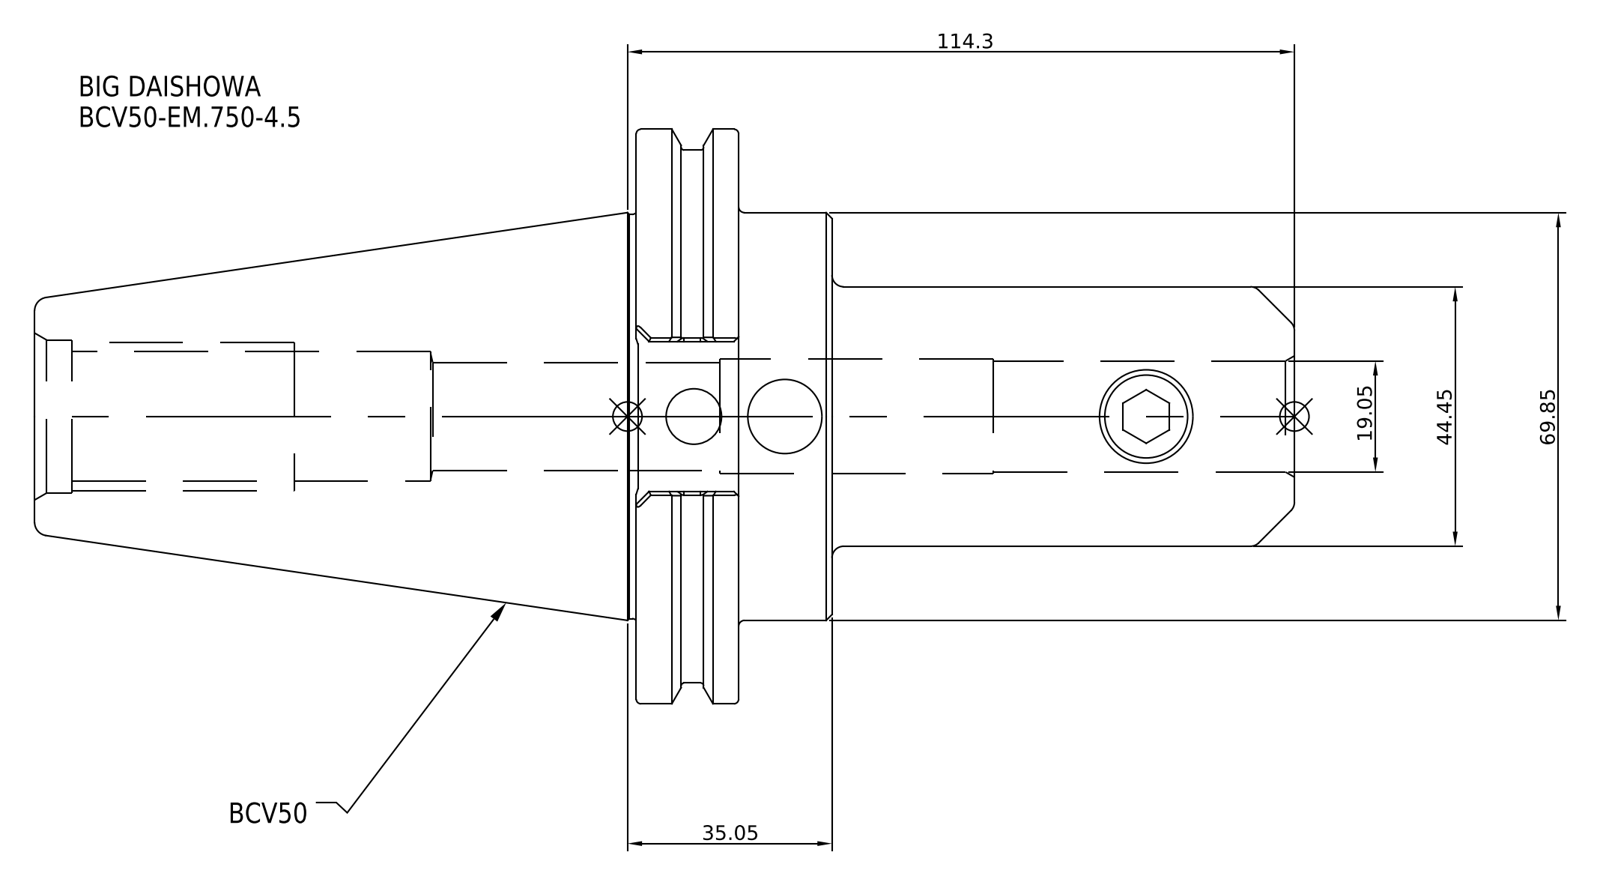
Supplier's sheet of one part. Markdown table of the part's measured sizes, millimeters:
| quantity | value |
| --- | --- |
| part name | BCV50-EM_750-4_5 |
| STEP written by | SolidWorks 2021 (CONFIG_CONTROL_DESIGN) |
| units | millimeters |
| bodies | 1 solid, 30 faces (8 planar, 14 cylindrical, 8 other) |
| overall size | 215.9 × 98.43 × 98.43 |
| volume | 540 244 mm³ |
| surface area | 56 187 mm² |
| round holes (diameter × count) | 19.05 × 1 |
| round bosses / shafts (diameter × count) | 98.43 × 1, 91.29 × 1, 69.85 × 1, 44.45 × 1 |
| main face-to-face distances | 17.55, 16, 33.55, 136.65, 120.65, 103.1, 79.25, 95.25, 112.8, 215.9 |
